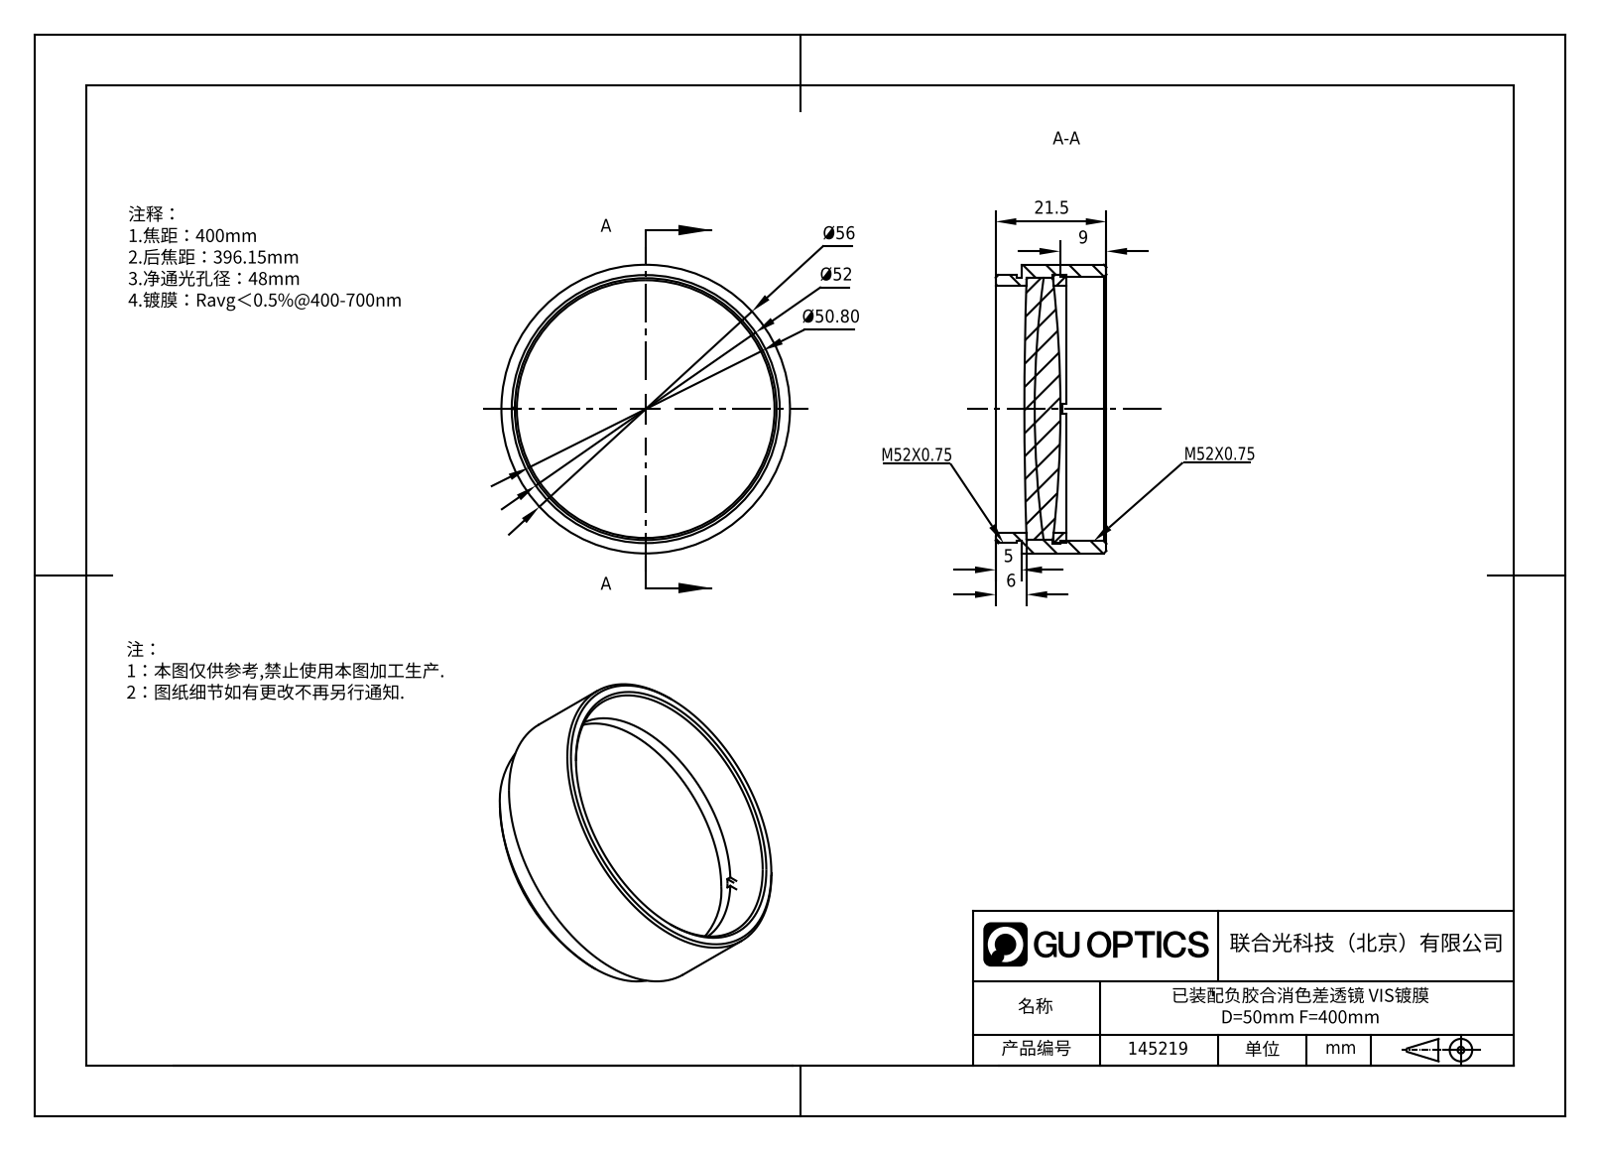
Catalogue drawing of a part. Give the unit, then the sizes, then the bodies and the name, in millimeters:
Units: millimetres
Overall size (bounding box): 56 × 56 × 21.5
Round holes (diameter × count): ⌀48 ×1, ⌀51.25 ×1, ⌀52.1 ×1
Round bosses / shafts (diameter × count): ⌀56 ×1, ⌀52 ×1, ⌀51 ×1, ⌀50.8 ×1
Main face-to-face distances: 5, 6, 8.76, 1, 6.26, 2.5, 11.26, 13.76, 21.5, 16.5
Volume: 21 393 mm³ · Surface area: 18 884 mm²
Bodies: 4 solids, 58 faces (16 planar, 22 cylindrical, 20 other)
Part name (STEP PRODUCT): M52x0.75安装环-PN35002-LM508-D1; M52x0.75ѹȦ; APD-ML50-400-VIS; GL31-050B-400-VIS_Solidworks
STEP written by: SolidWorks 2022 (AUTOMOTIVE_DESIGN)
